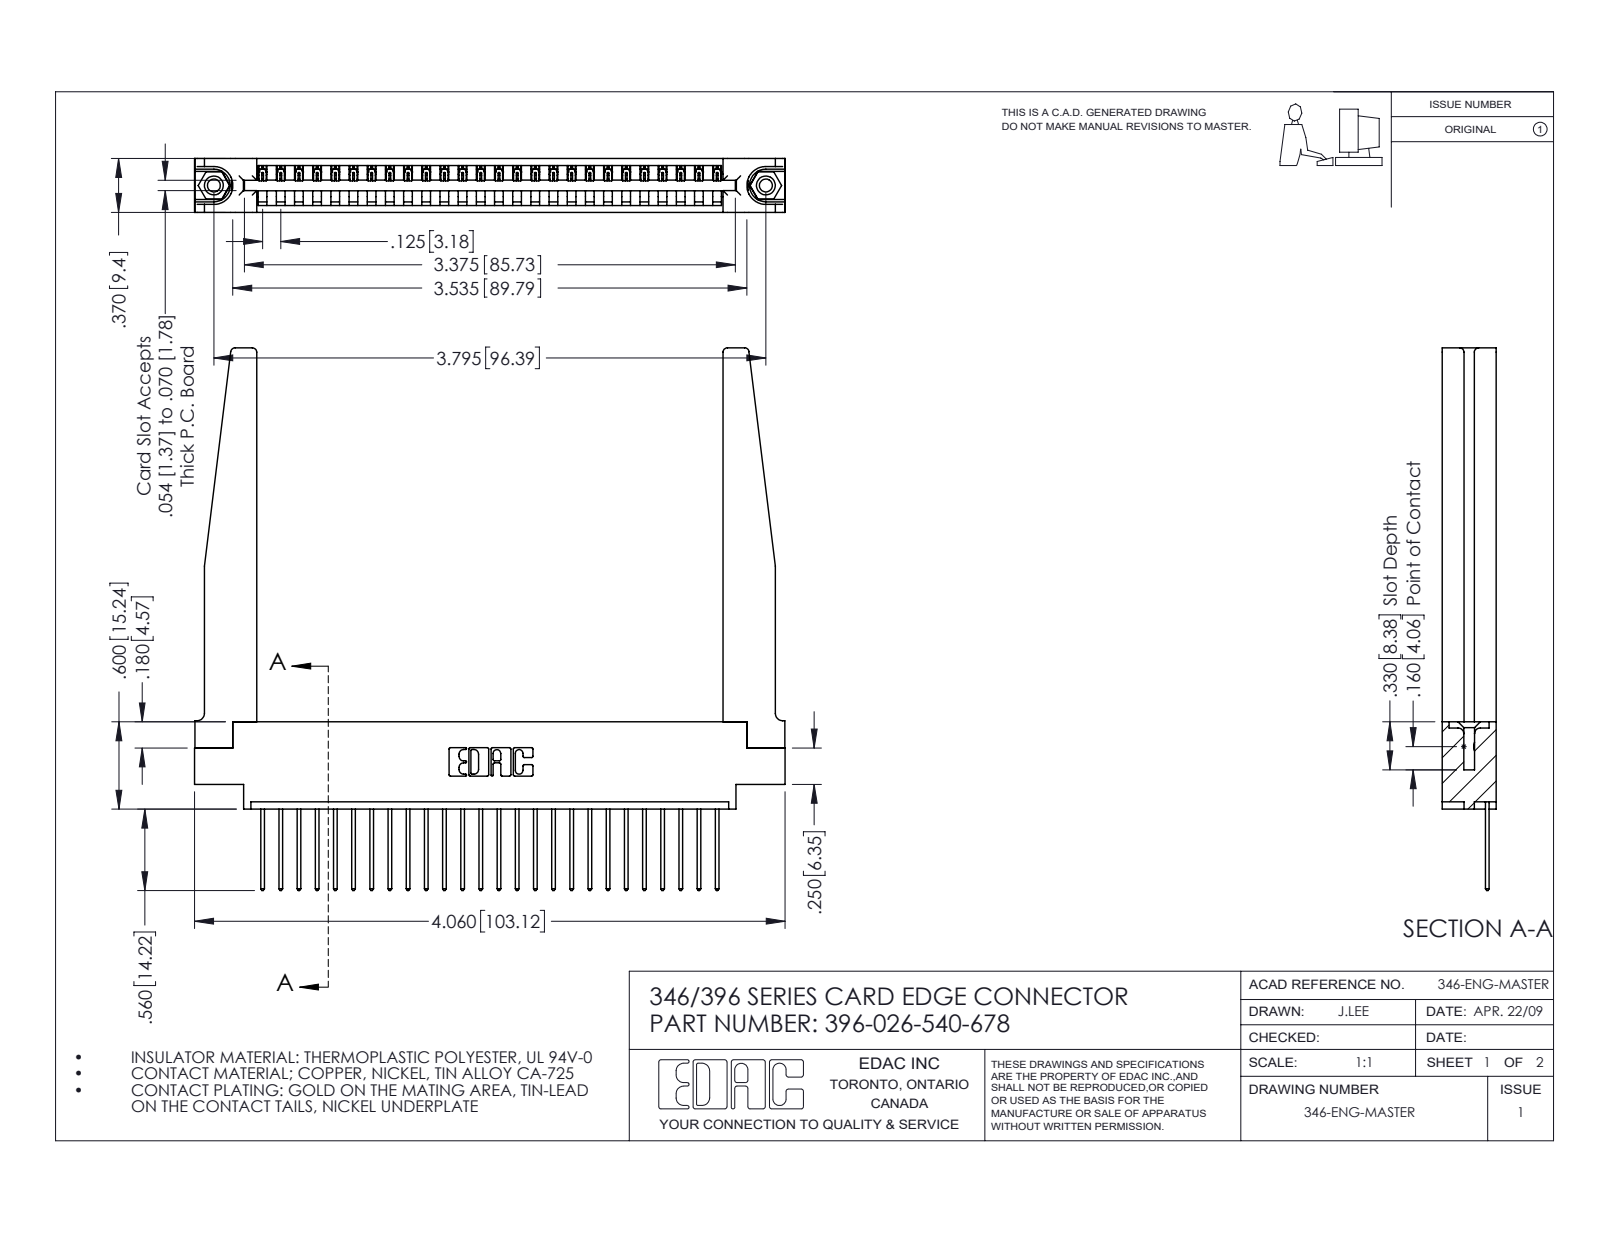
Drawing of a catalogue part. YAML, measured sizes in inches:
part_name: "345-250-001_345-250-001-102; 396-026-540-678; 346-220-078_345-220-078; 345-292-001_345-293-140 (+1 more)"
step_written_by: "SolidWorks 2016 (CONFIG_CONTROL_DESIGN)"
units: inches
bodies: {solids: 31, faces: 1868, planar: 1262, cylindrical: 554, other: 52}
overall_size: [4.06, 3.73, 0.37]
volume: 1.01
surface_area: 29.2
round_holes:
  - {diameter: 0.089, count: 2}
  - {diameter: 0.125, count: 2}
  - {diameter: 0.156, count: 2}
  - {diameter: 0.064, count: 1}
round_bosses_or_shafts:
  - {diameter: 0.155, count: 2}
partial_cylinders:
  - {radius: 0.006, count: 52}
  - {radius: 0.01, count: 52}
  - {radius: 0.01, count: 22}
  - {radius: 0.03, count: 8}
  - {radius: 0.007, count: 6}
  - {radius: 0.031, count: 6}
  - {radius: 0.026, count: 3}
  - {radius: 0.031, count: 2}
face_to_face_distances: [0.37, 0.048, 0.322, 0.072, 0.148, 0.15, 0.25, 0.298, 0.025, 0.222]
hole_center_spacings: [0.246, 3.587, 3.795]
